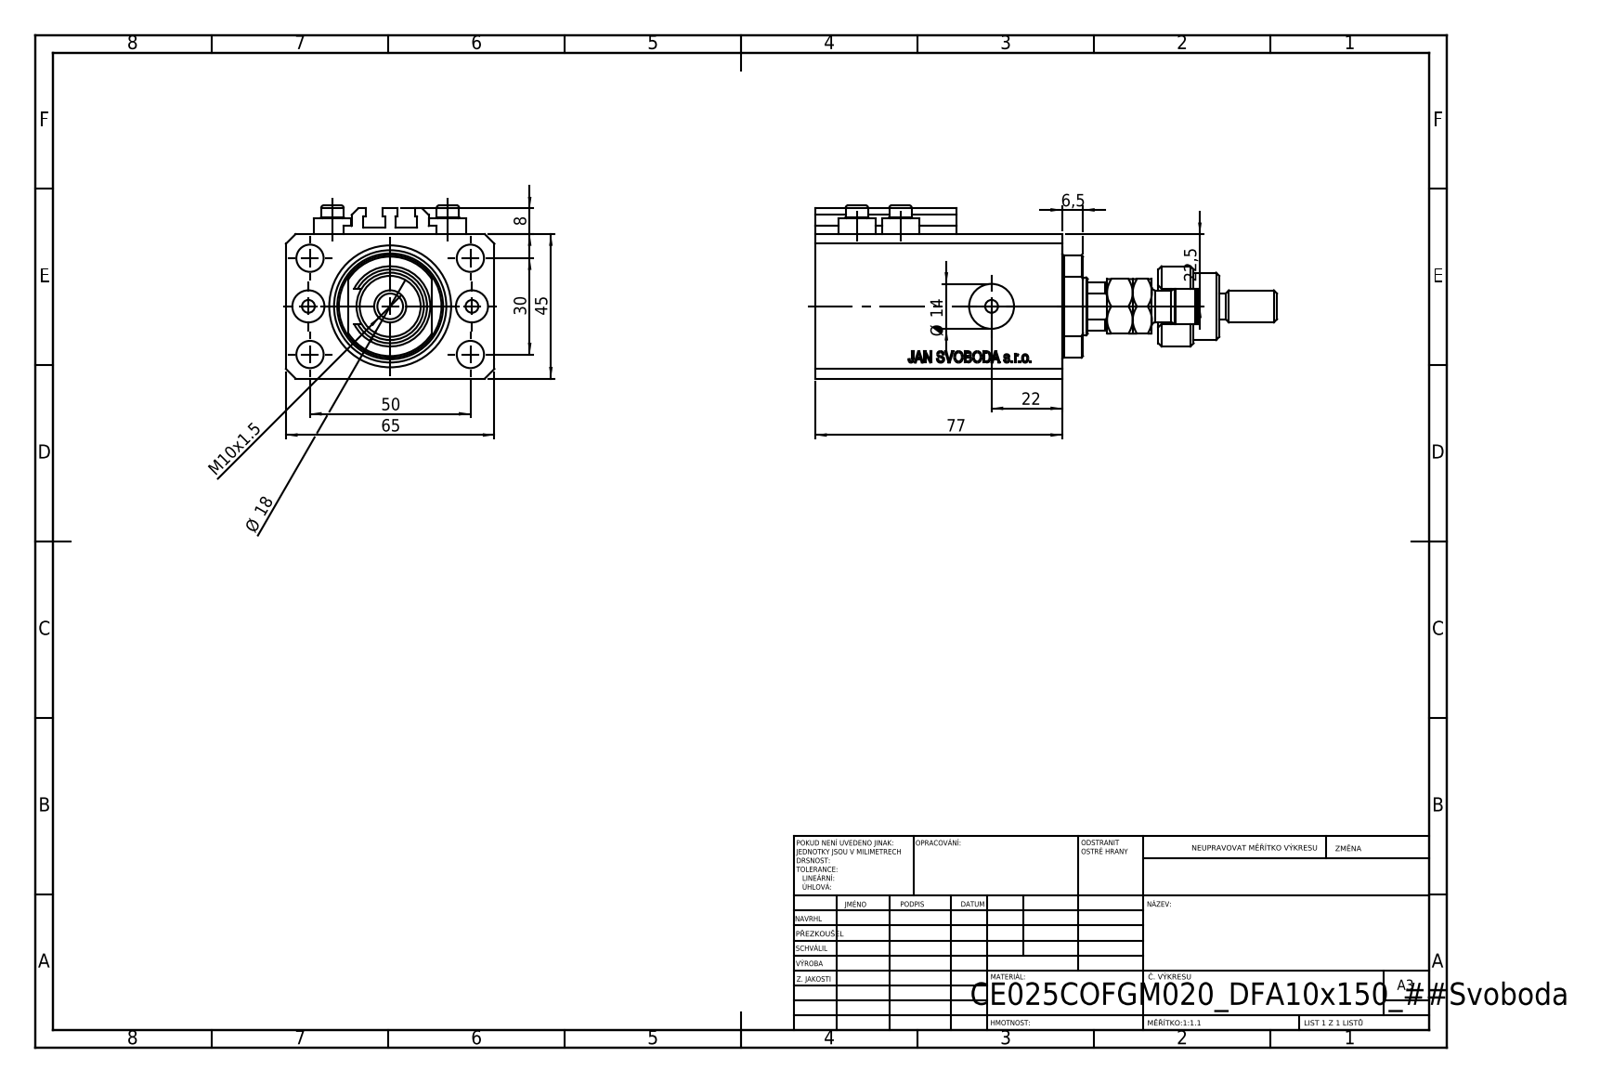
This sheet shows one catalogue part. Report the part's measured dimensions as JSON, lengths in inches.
{"part_name": "V250CE_C_VCP; V250CE_VC_C; FEMALE_PART_FOR_DFA; ALLEN BOLT V250CE (+2 more)", "step_written_by": "SolidWorks 2019 (CONFIG_CONTROL_DESIGN)", "units": "inches", "bodies": {"solids": 10, "faces": 1119, "planar": 532, "cylindrical": 99, "other": 488}, "overall_size": [5.669, 2.559, 2.126], "volume_in3": 13.65, "surface_area_in2": 97.2, "round_holes": [[0.157, 8], [0.335, 5], [0.394, 2], [0.551, 2], [0.709, 1], [1.496, 1]], "round_bosses_or_shafts": [[0.457, 4], [0.276, 4], [0.984, 1], [0.827, 1], [0.63, 1], [0.394, 1], [0.315, 1]], "partial_cylinders_radius": [[0.008, 10], [0.217, 1], [0.335, 1], [0.344, 1], [0.63, 1]], "face_to_face_distances": [1.772, 0.551, 2.559, 2.48, 3.031, 0.118, 0.272, 2.209, 2.76, 1.85], "hole_center_spacings": [0.591, 1.148, 2.074, 0.535, 1.004, 1.181, 1.417, 1.515]}
